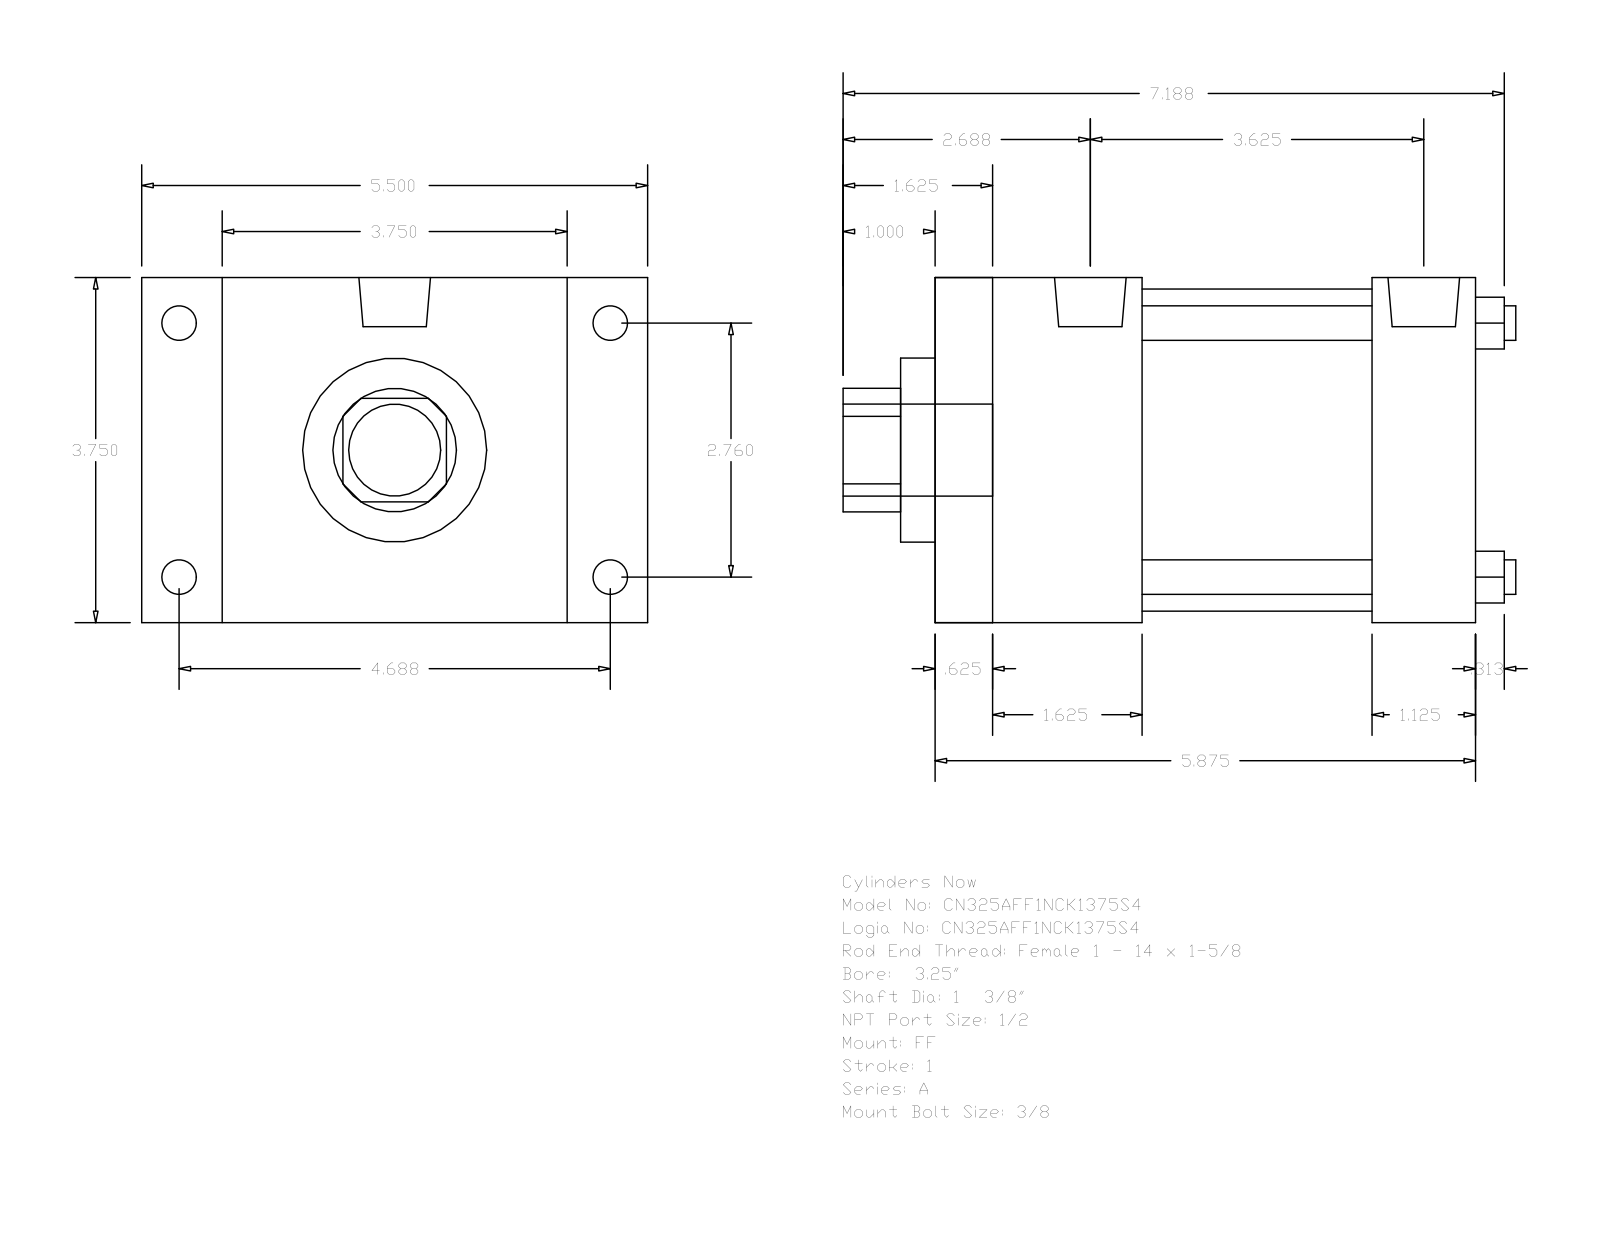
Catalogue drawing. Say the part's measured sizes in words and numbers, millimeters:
The part is named "A_FF__0325_1.375". Its 3-D file was written by "GSSL Pune (CONFIG_CONTROL_DESIGN)". It is 0 solids with 92 faces: 64 planar, 28 cylindrical and 0 other. Overall it measures 185.74 by 139.7 by 95.25 millimeters. Round holes: 4 of diameter 9.53, 1 of diameter 34.92, 1 of diameter 50.8, 1 of diameter 88.9. Round bosses or shafts: 4 of diameter 9.53, 4 of diameter 8.73, 2 of diameter 19.77, 1 of diameter 25.4. Partial cylindrical surfaces (rounded edges, fillets, slot ends): 1 of radius 17.06. The main face-to-face distances are 95.24, 149.22, 133.35, 15.87, 22.23, 117.47, 28.57, 57.15, 120.65, 41.28. The hole center spacings are 49.57, 70.1, 99.14.
